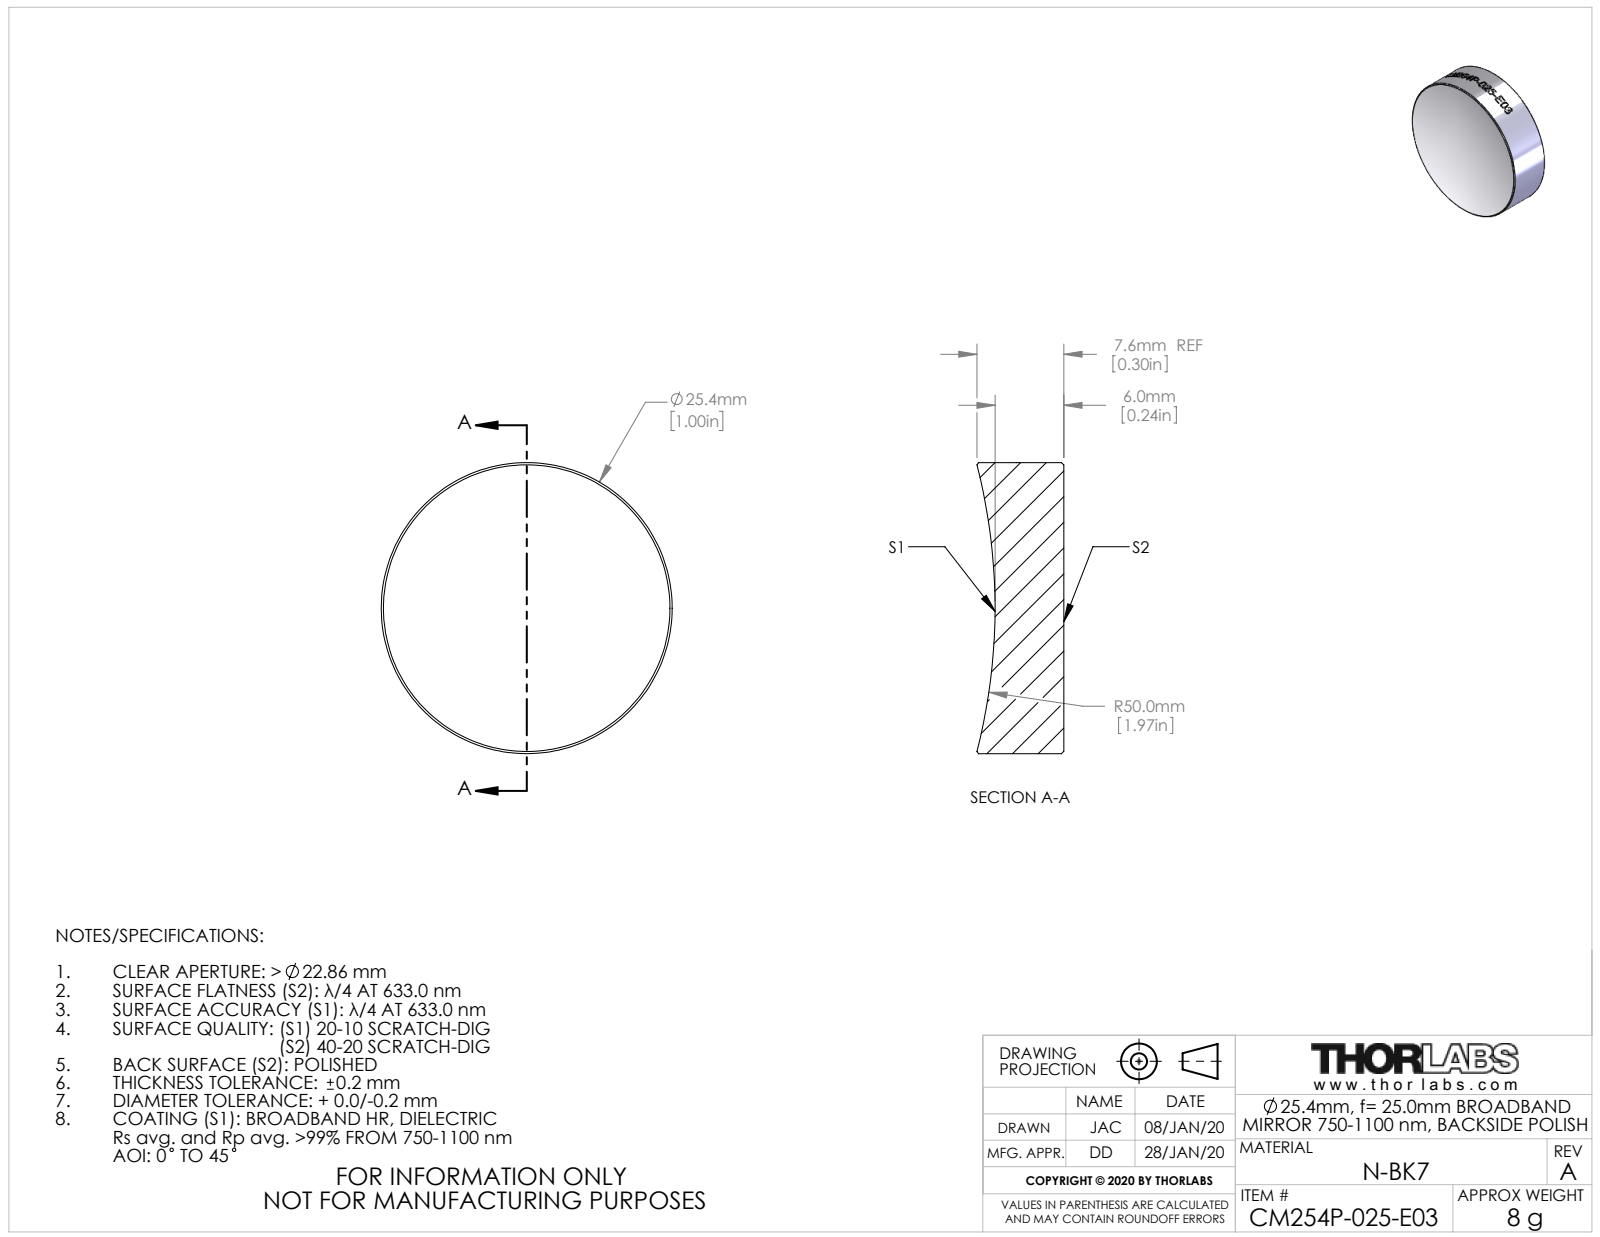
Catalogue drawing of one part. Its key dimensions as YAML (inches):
part_name: "TTN201386-E0W"
step_written_by: "SolidWorks 2018 (CONFIG_CONTROL_DESIGN)"
units: inches
bodies: {solids: 1, faces: 27, planar: 1, cylindrical: 20, other: 6}
overall_size: [1, 1, 0.299]
volume: 0.211
surface_area: 2.496
round_bosses_or_shafts:
  - {diameter: 1, count: 1}
